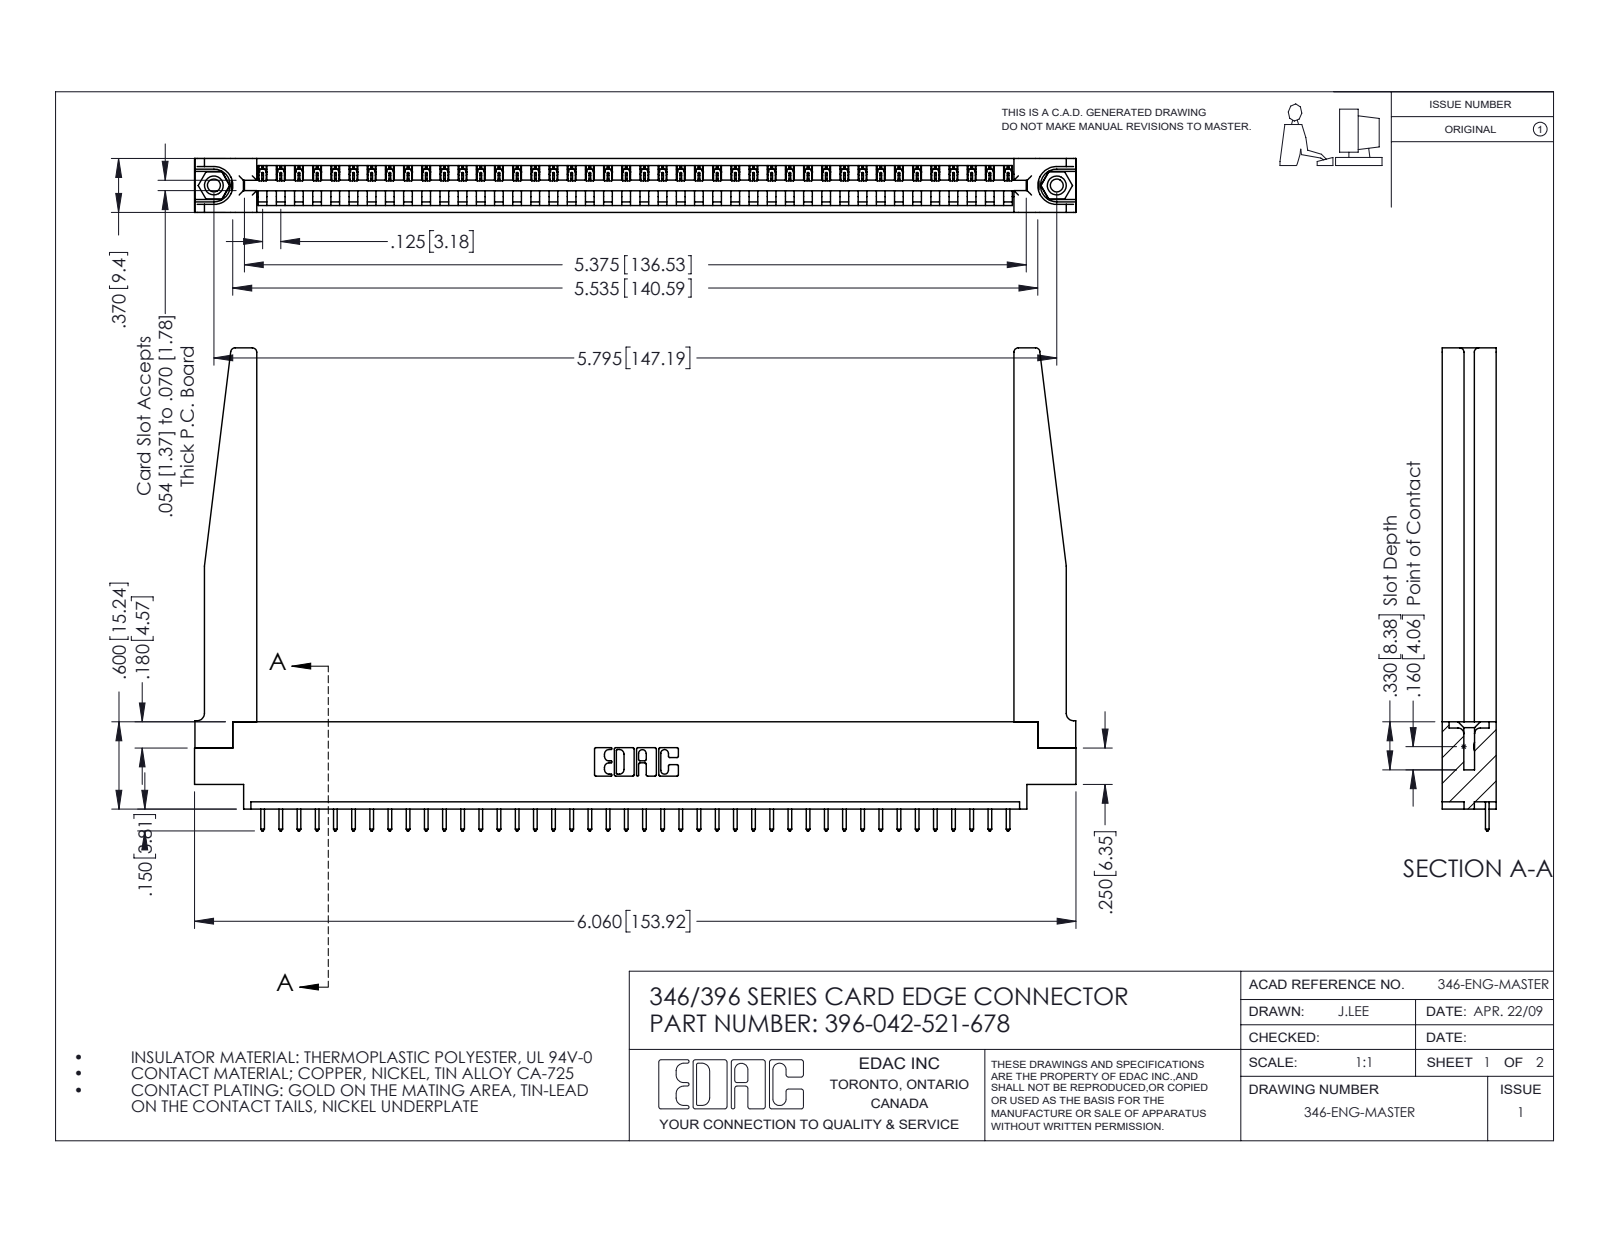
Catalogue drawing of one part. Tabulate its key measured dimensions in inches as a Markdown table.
| quantity | value |
| --- | --- |
| part name | 345-250-001_345-250-001-102; 345-292-001_345-293-121; 346 Part_0.170 Offset - 0.156 Dia-TH; 346-220-078_345-220-078 (+1 more) |
| STEP written by | SolidWorks 2016 (CONFIG_CONTROL_DESIGN) |
| units | inches |
| bodies | 47 solids, 2796 faces (1902 planar, 842 cylindrical, 52 other) |
| overall size | 6.06 × 3.32 × 0.37 |
| volume | 1.304 in³ |
| surface area | 37.66 in² |
| round holes (diameter × count) | 0.089 × 2, 0.125 × 2, 0.156 × 2, 0.064 × 1 |
| round bosses / shafts (diameter × count) | 0.155 × 2 |
| partial cylindrical surfaces (radius × count) | 0.006 × 84, 0.01 × 84, 0.01 × 22, 0.03 × 8, 0.007 × 6, 0.031 × 6, 0.026 × 3, 0.031 × 2 |
| main face-to-face distances | 0.37, 0.048, 0.322, 0.072, 0.148, 0.15, 0.25, 0.298, 0.025, 0.222 |
| hole center spacings | 0.246, 5.586, 5.795 |
